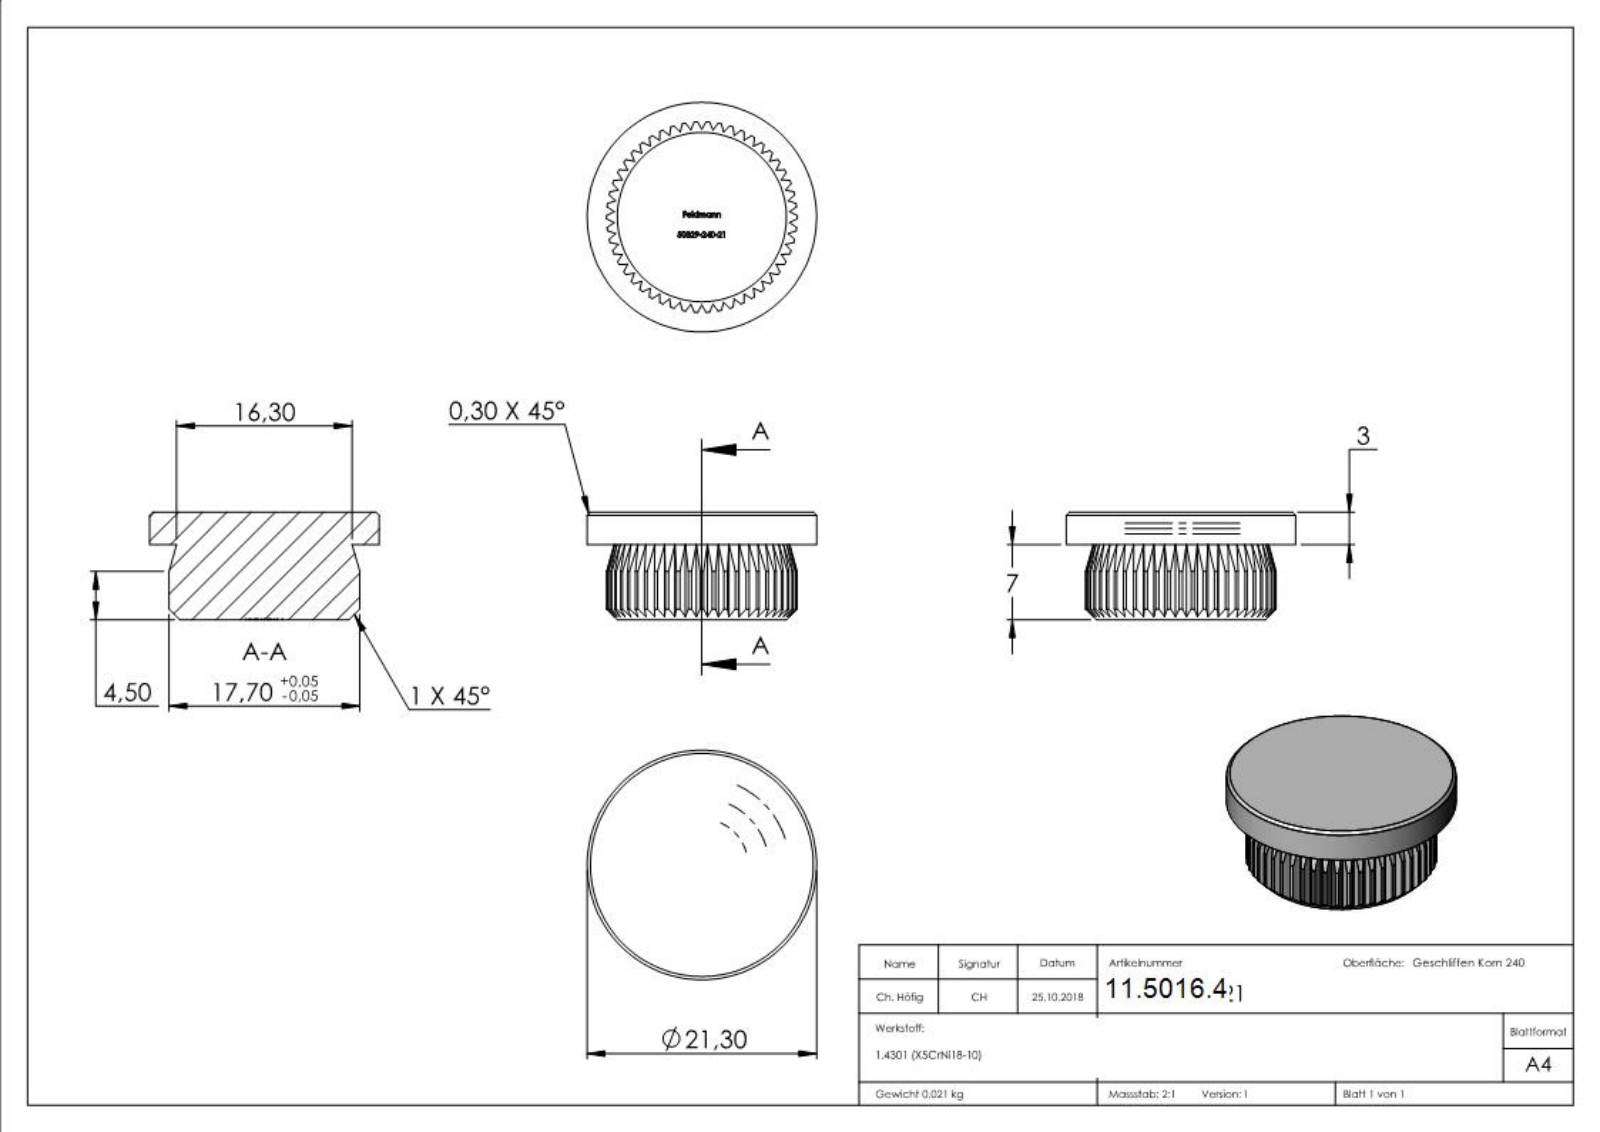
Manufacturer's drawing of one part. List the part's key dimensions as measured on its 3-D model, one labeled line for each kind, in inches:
Part name (STEP PRODUCT): 50329-240-21
STEP written by: SolidWorks 2015 (CONFIG_CONTROL_DESIGN)
Units: inches
Bodies: 1 solid, 462 faces (241 planar, 52 cylindrical, 169 other)
Overall size (bounding box): 0.839 × 0.839 × 0.394
Volume: 0.162 in³ · Surface area: 2.316 in²
Round bosses / shafts (diameter × count): ⌀0.839 ×1
Partial cylindrical surfaces — rounded edges, fillets, slot ends (radius × count): R0.348 ×1
Main face-to-face distances: 0.394, 0.276, 0.118, 0.321, 0.32, 0.272, 0.39, 0.065, 0.072, 0.026
